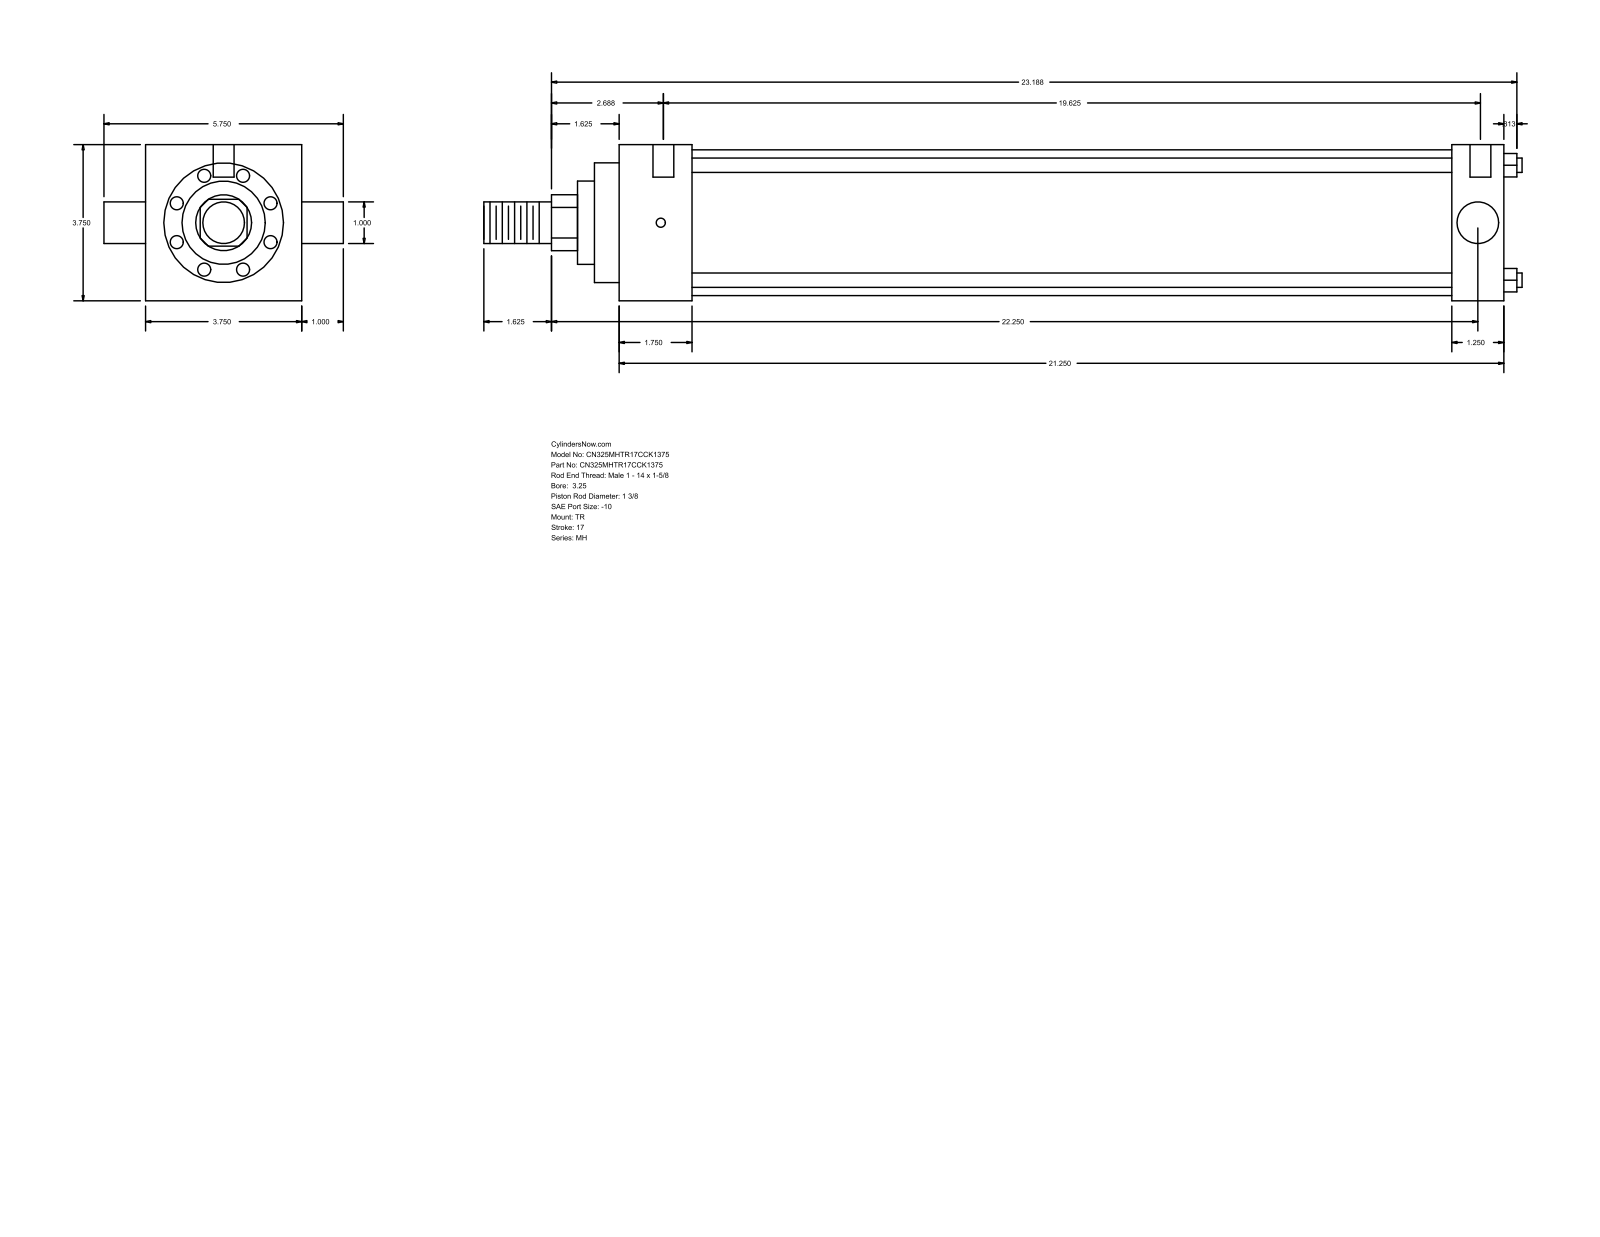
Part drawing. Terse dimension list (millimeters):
name: MH_TR__0325_1.375
written by: GSSL Pune (CONFIG_CONTROL_DESIGN)
unit: mm
bodies: 0 solids, 86 faces (61 planar, 25 cylindrical, 0 other)
size: 633.41 × 146.05 × 95.25
holes: 3× ⌀5.56, 2× ⌀12.7
bosses: 4× ⌀8.76, 2× ⌀25.4, 1× ⌀88.9, 1× ⌀73.03, 1× ⌀50.8, 1× ⌀34.92
rounds: 1× R17.06
face distances: 95.24, 539.75, 44.45, 508, 463.55, 495.3, 31.75, 15.08, 59.53, 523.08
hole spacings: 1.59, 4.76, 498.48, 500.07, 503.24, 504.83
